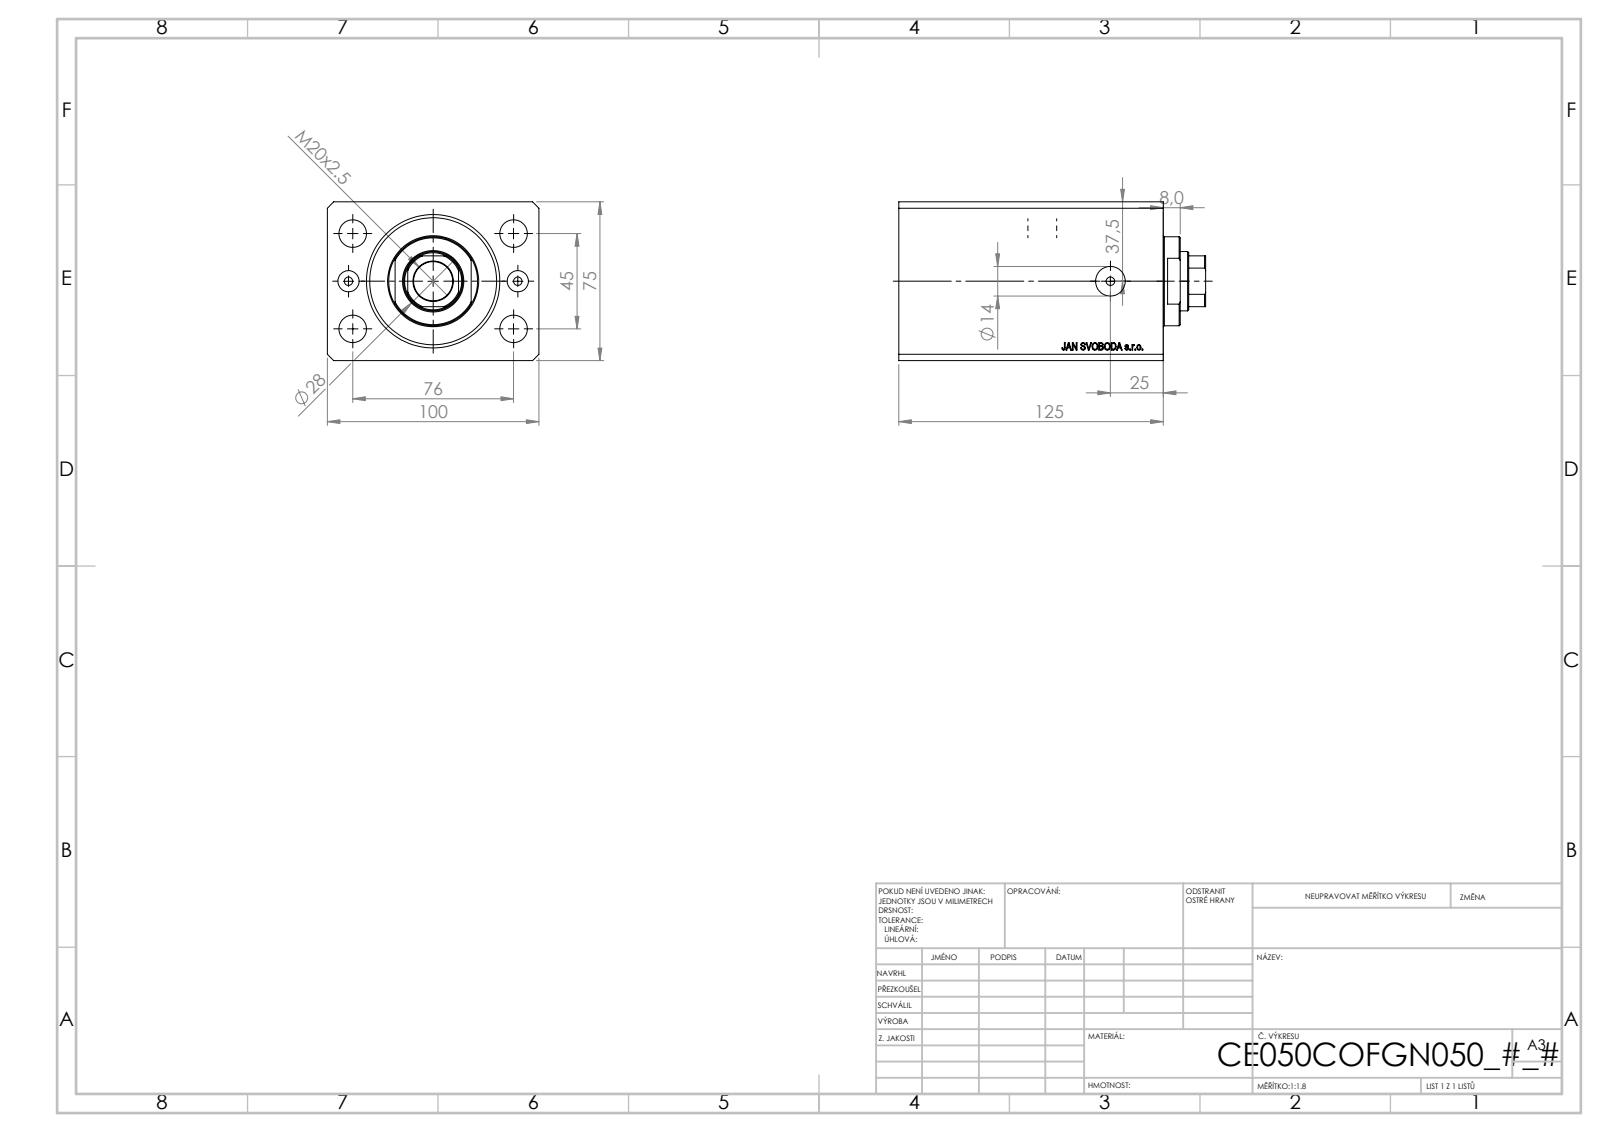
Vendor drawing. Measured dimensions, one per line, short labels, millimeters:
name: V250CE_C_Body; V250CE_VC_C; V250CE_C_VCP
written by: SolidWorks 2019 (CONFIG_CONTROL_DESIGN)
unit: mm
bodies: 3 solids, 864 faces (428 planar, 44 cylindrical, 392 other)
size: 144.9 × 100 × 75
volume: 805 780 mm³; area: 132 517 mm²
holes: 4× ⌀4, 4× ⌀13, 2× ⌀10, 2× ⌀14, 1× ⌀18.5, 1× ⌀28, 1× ⌀50, 1× ⌀63
bosses: 1× ⌀42
rounds: 1× R13.5
face distances: 75, 100, 125, 11.9, 113.1, 86.5, 98.4, 26.6, 48.4, 36.5
hole spacings: 22.59, 44.16, 81.18, 40, 45, 76, 88.32, 75
